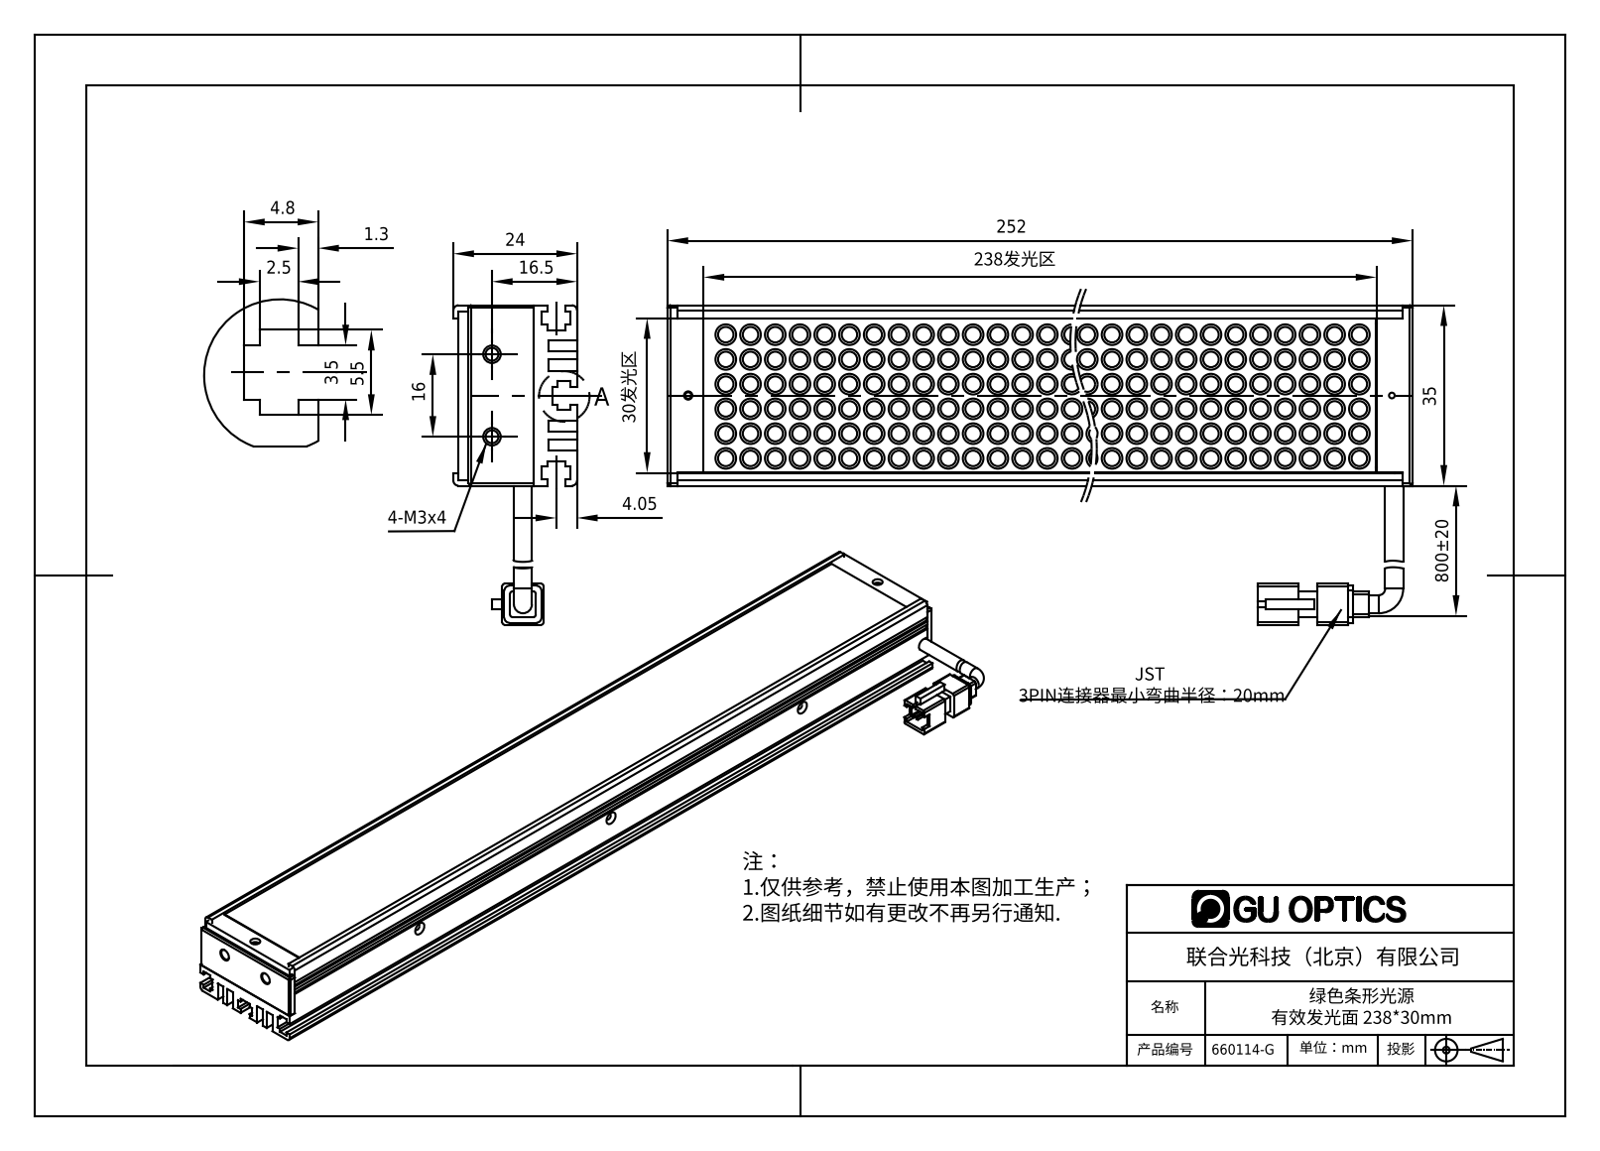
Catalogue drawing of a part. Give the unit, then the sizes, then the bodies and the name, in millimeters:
Units: millimetres
Overall size (bounding box): 252 × 62 × 24
Round holes (diameter × count): ⌀1.6 ×5, ⌀1.7 ×3, ⌀1.5 ×2, ⌀2.5 ×2, ⌀2.8 ×2, ⌀3 ×2, ⌀1.1 ×1, ⌀1.25 ×1, ⌀2 ×1
Round bosses / shafts (diameter × count): ⌀4 ×294, ⌀3 ×294, ⌀3.5 ×2
Partial cylindrical surfaces — rounded edges, fillets, slot ends (radius × count): R1 ×12, R0.5 ×8, R1.65 ×1
Main face-to-face distances: 2, 2.2, 8.6, 1, 2.5, 9, 4, 12.6, 14.6, 10.6
Hole centre spacings: 244, 7, 47.03, 47.31, 75, 122.01, 122.12, 197.01
Volume: 111 778 mm³ · Surface area: 127 737 mm²
Bodies: 8 solids, 2226 faces (562 planar, 1263 cylindrical, 401 other)
Part name (STEP PRODUCT): 660114-G
STEP written by: SolidWorks 2016 (AUTOMOTIVE_DESIGN)
